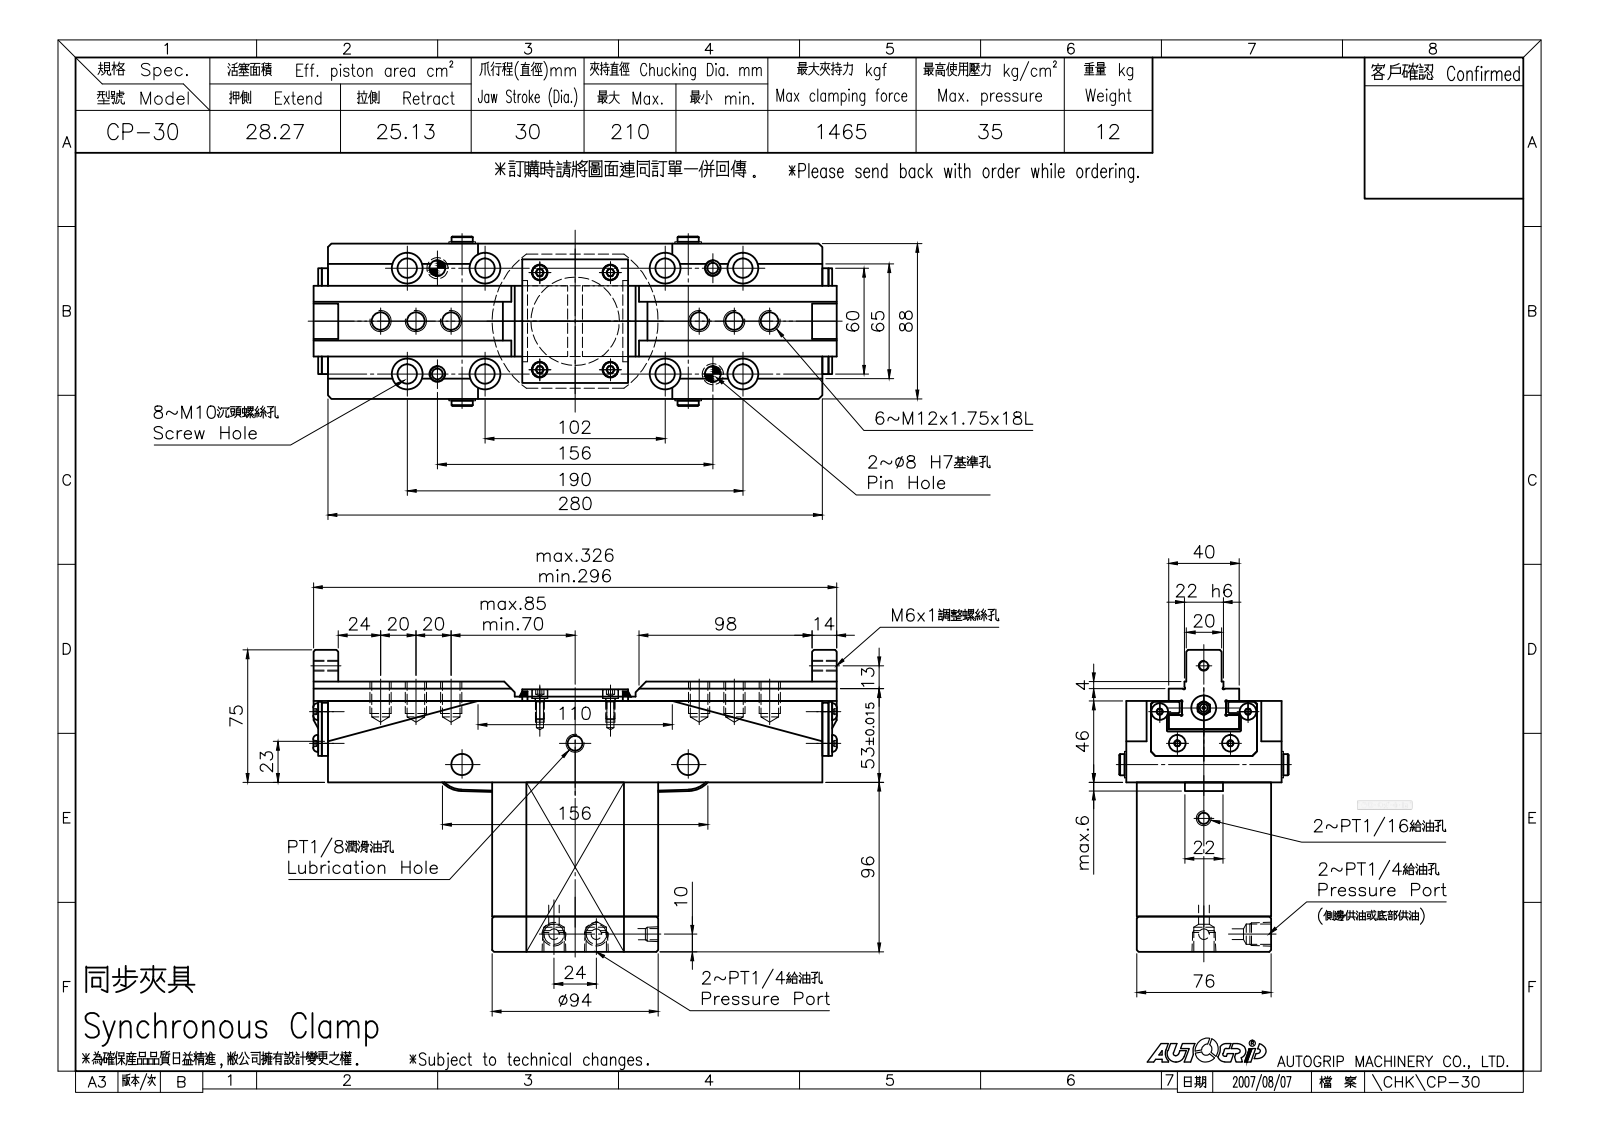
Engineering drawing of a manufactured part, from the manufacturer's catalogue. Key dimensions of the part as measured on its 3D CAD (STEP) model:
Part name (STEP PRODUCT): CF-CP-30-06010; CF-CP-30-11000; CF-CP-30; CF-CP-30-01000 (+8 more)
STEP written by: SolidWorks 2020 (CONFIG_CONTROL_DESIGN)
Units: millimetres
Bodies: 36 solids, 1047 faces (476 planar, 315 cylindrical, 256 other)
Overall size (bounding box): 296.5 × 171 × 96
Volume: 1 755 000 mm³ · Surface area: 289 445 mm²
Round holes (diameter × count): ⌀9 ×12, ⌀4.2 ×8, ⌀11 ×8, ⌀17.5 ×8, ⌀6 ×6, ⌀6.8 ×6, ⌀10.2 ×6, ⌀14 ×5, ⌀5.5 ×4, ⌀11.5 ×4, ⌀5 ×2, ⌀6.3 ×2
Round bosses / shafts (diameter × count): ⌀5 ×8, ⌀13 ×4, ⌀9.5 ×4, ⌀8.5 ×4, ⌀8 ×4, ⌀12 ×2, ⌀6 ×1, ⌀3 ×1
Partial cylindrical surfaces — rounded edges, fillets, slot ends (radius × count): R4 ×2, R15 ×2, R47 ×1
Main face-to-face distances: 46, 31.5, 56.5, 76, 30, 16, 6, 25, 106, 122
Hole centre spacings: 49.2, 94.11, 43.86, 60, 6.59, 17, 20, 24
